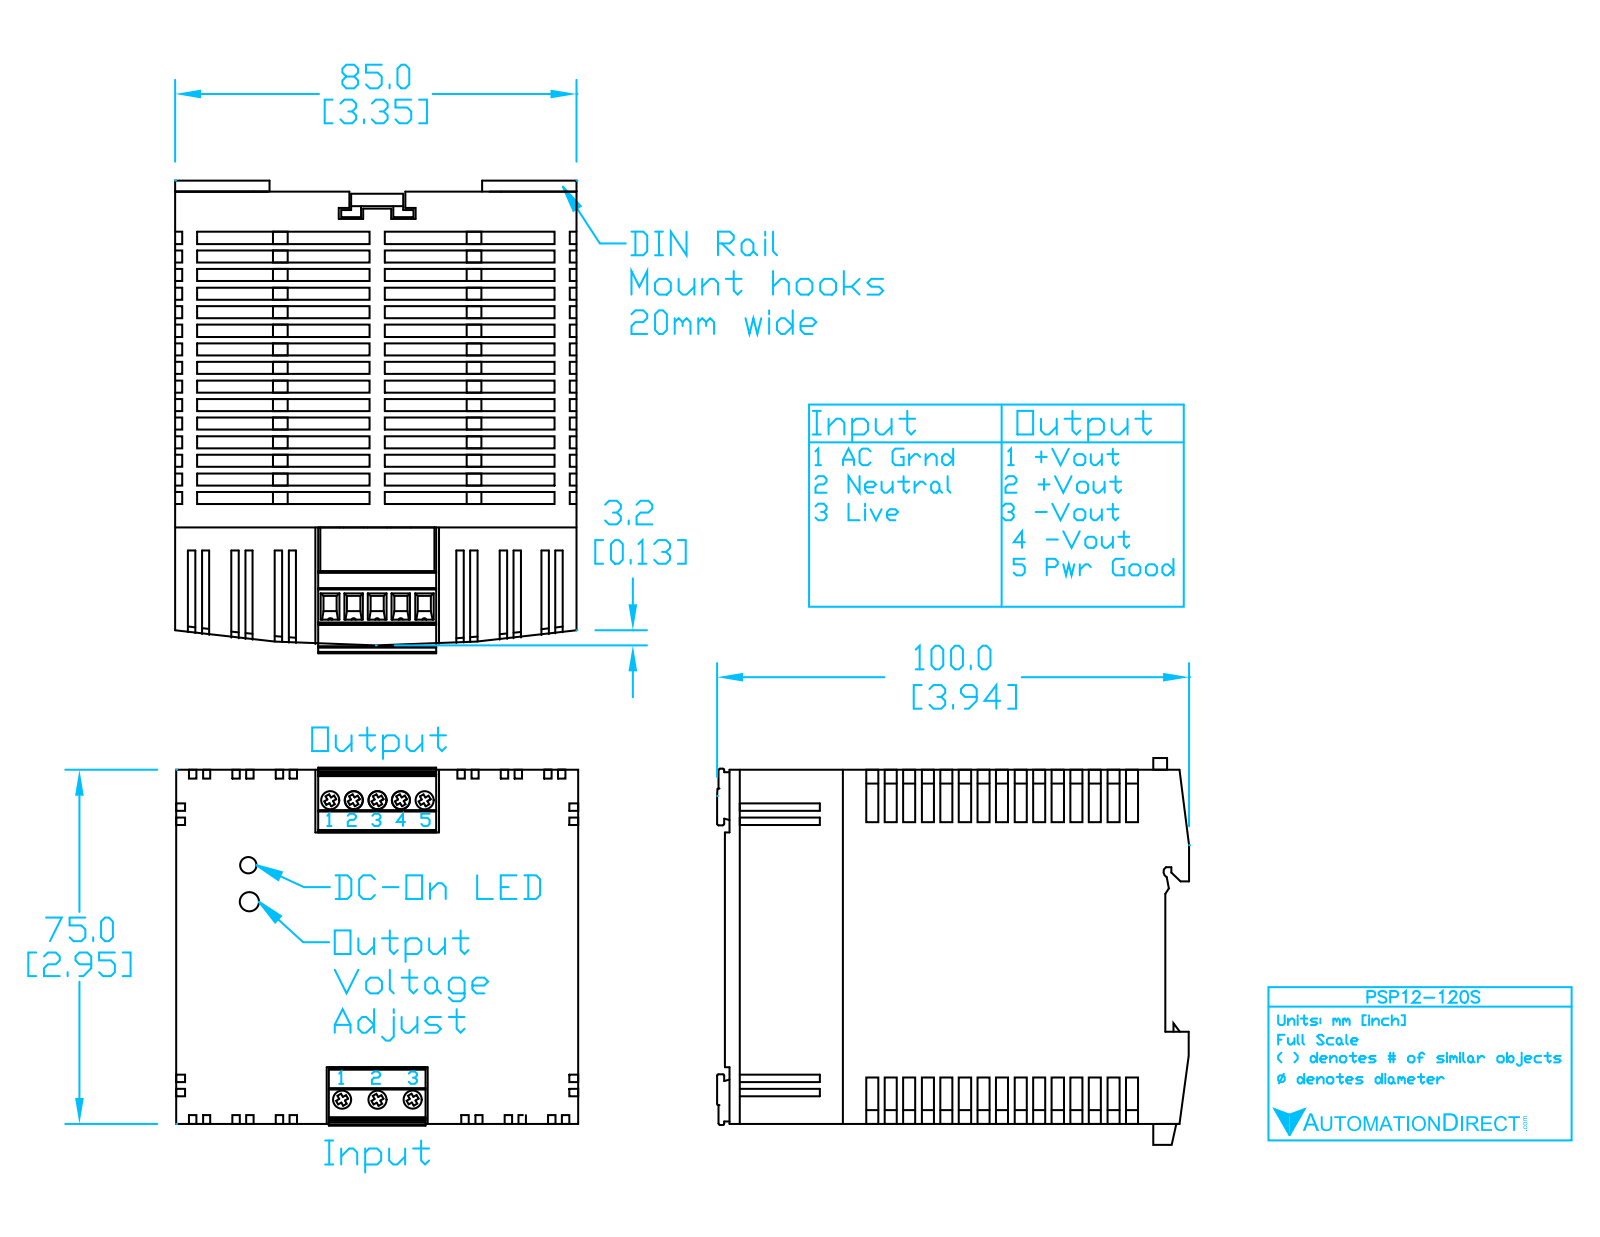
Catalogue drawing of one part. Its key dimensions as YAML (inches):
part_name: "PSP12-120S"
step_written_by: "SolidWorks 2011 (CONFIG_CONTROL_DESIGN)"
units: inches
bodies: {solids: 6, faces: 320, planar: 249, cylindrical: 0, other: 71}
overall_size: [4.008, 3.346, 3.15]
volume: 43.18
surface_area: 111.1
face_to_face_distances: [2.953, 3.346, 2.711, 2.715, 0.558, 2.395, 2.35, 1.792, 0.603, 0.098]
